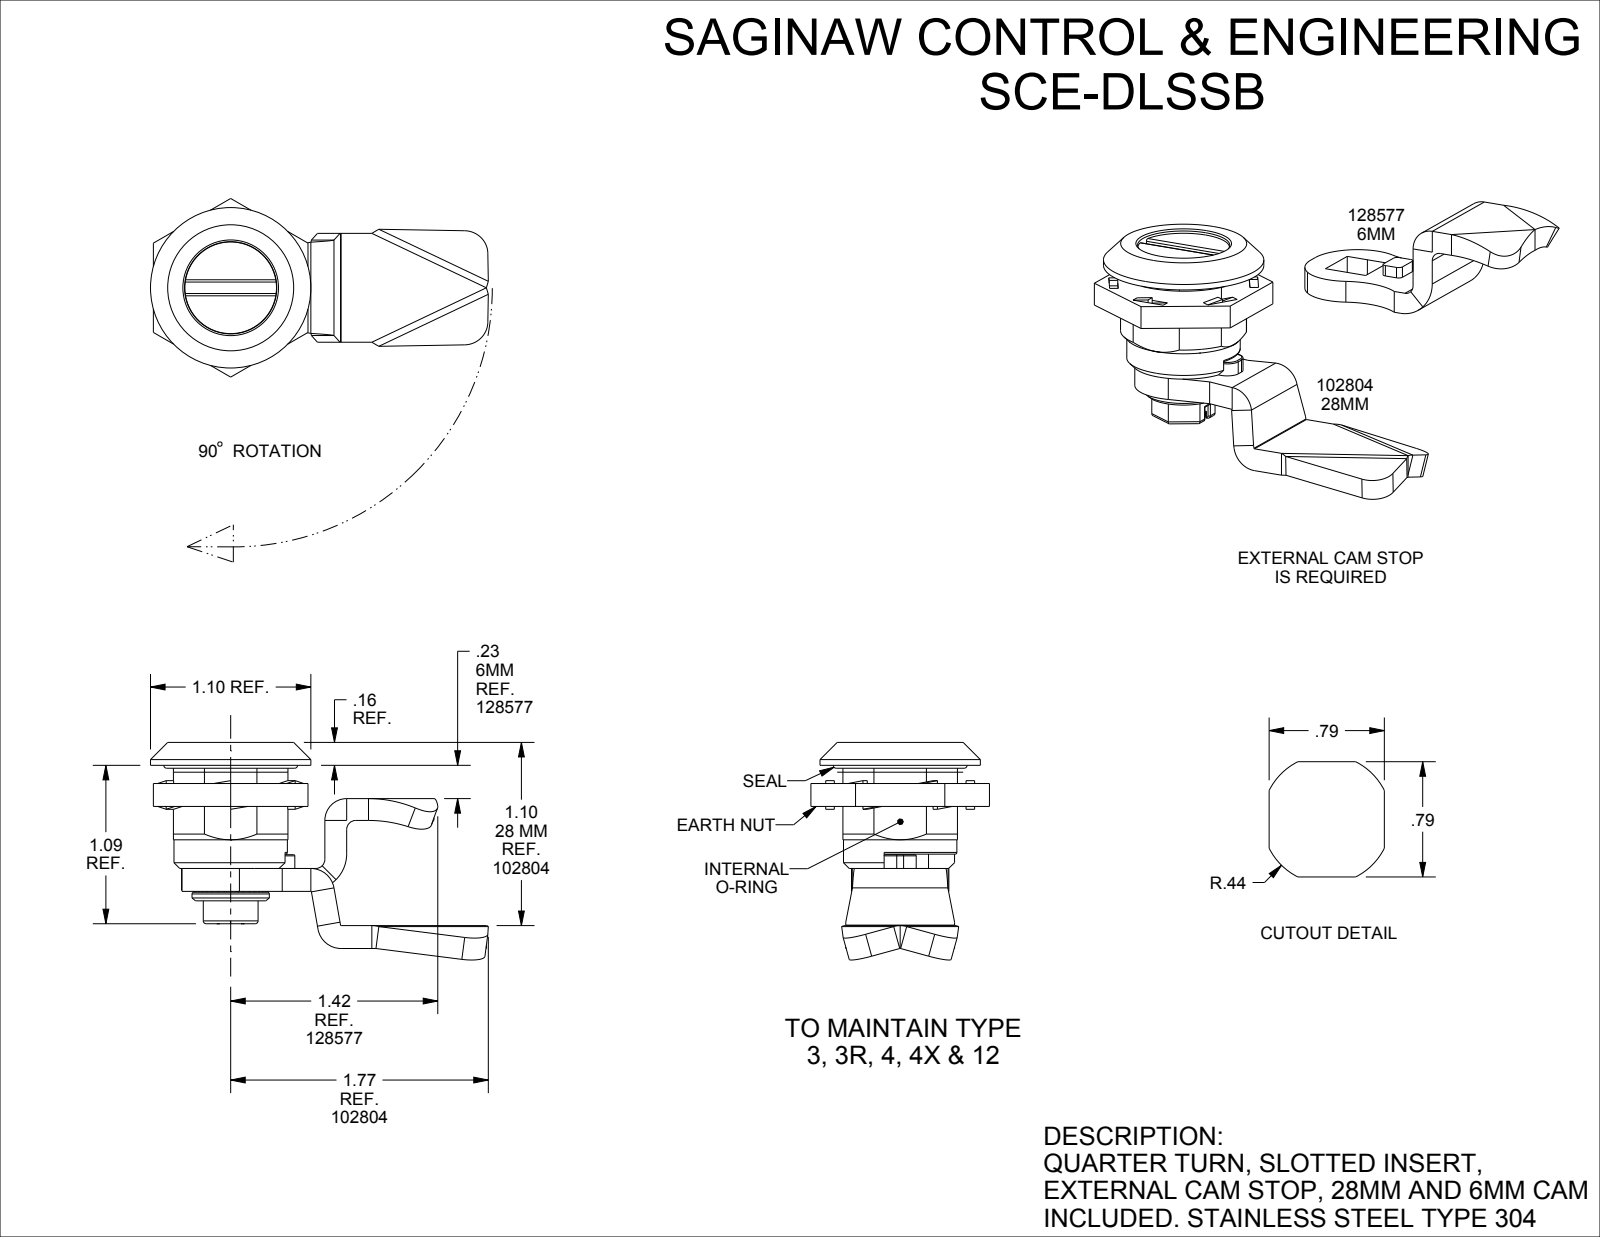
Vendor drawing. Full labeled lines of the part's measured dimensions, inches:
Part name (STEP PRODUCT): SCE-DLSB
STEP written by: SolidWorks 2021 (AUTOMOTIVE_DESIGN)
Units: inches
Bodies: 8 solids, 366 faces (187 planar, 116 cylindrical, 63 other)
Overall size (bounding box): 3.334 × 2.322 × 1.924
Volume: 1.01 in³ · Surface area: 19.36 in²
Round holes (diameter × count): ⌀0.197 ×1, ⌀0.315 ×1, ⌀0.394 ×1, ⌀0.634 ×1, ⌀0.795 ×1
Round bosses / shafts (diameter × count): ⌀1.102 ×1, ⌀0.78 ×1, ⌀0.63 ×1, ⌀0.531 ×1, ⌀0.504 ×1, ⌀0.39 ×1, ⌀0.217 ×1
Partial cylindrical surfaces — rounded edges, fillets, slot ends (radius × count): R0.012 ×30, R0.02 ×12, R0.03 ×4, R0.157 ×4, R0.3 ×4, R0.004 ×2, R0.008 ×2, R0.016 ×2
Main face-to-face distances: 0.157, 0.976, 0.393, 0.584, 0.15, 1.259, 0.282, 0.866, 0.48, 0.709
